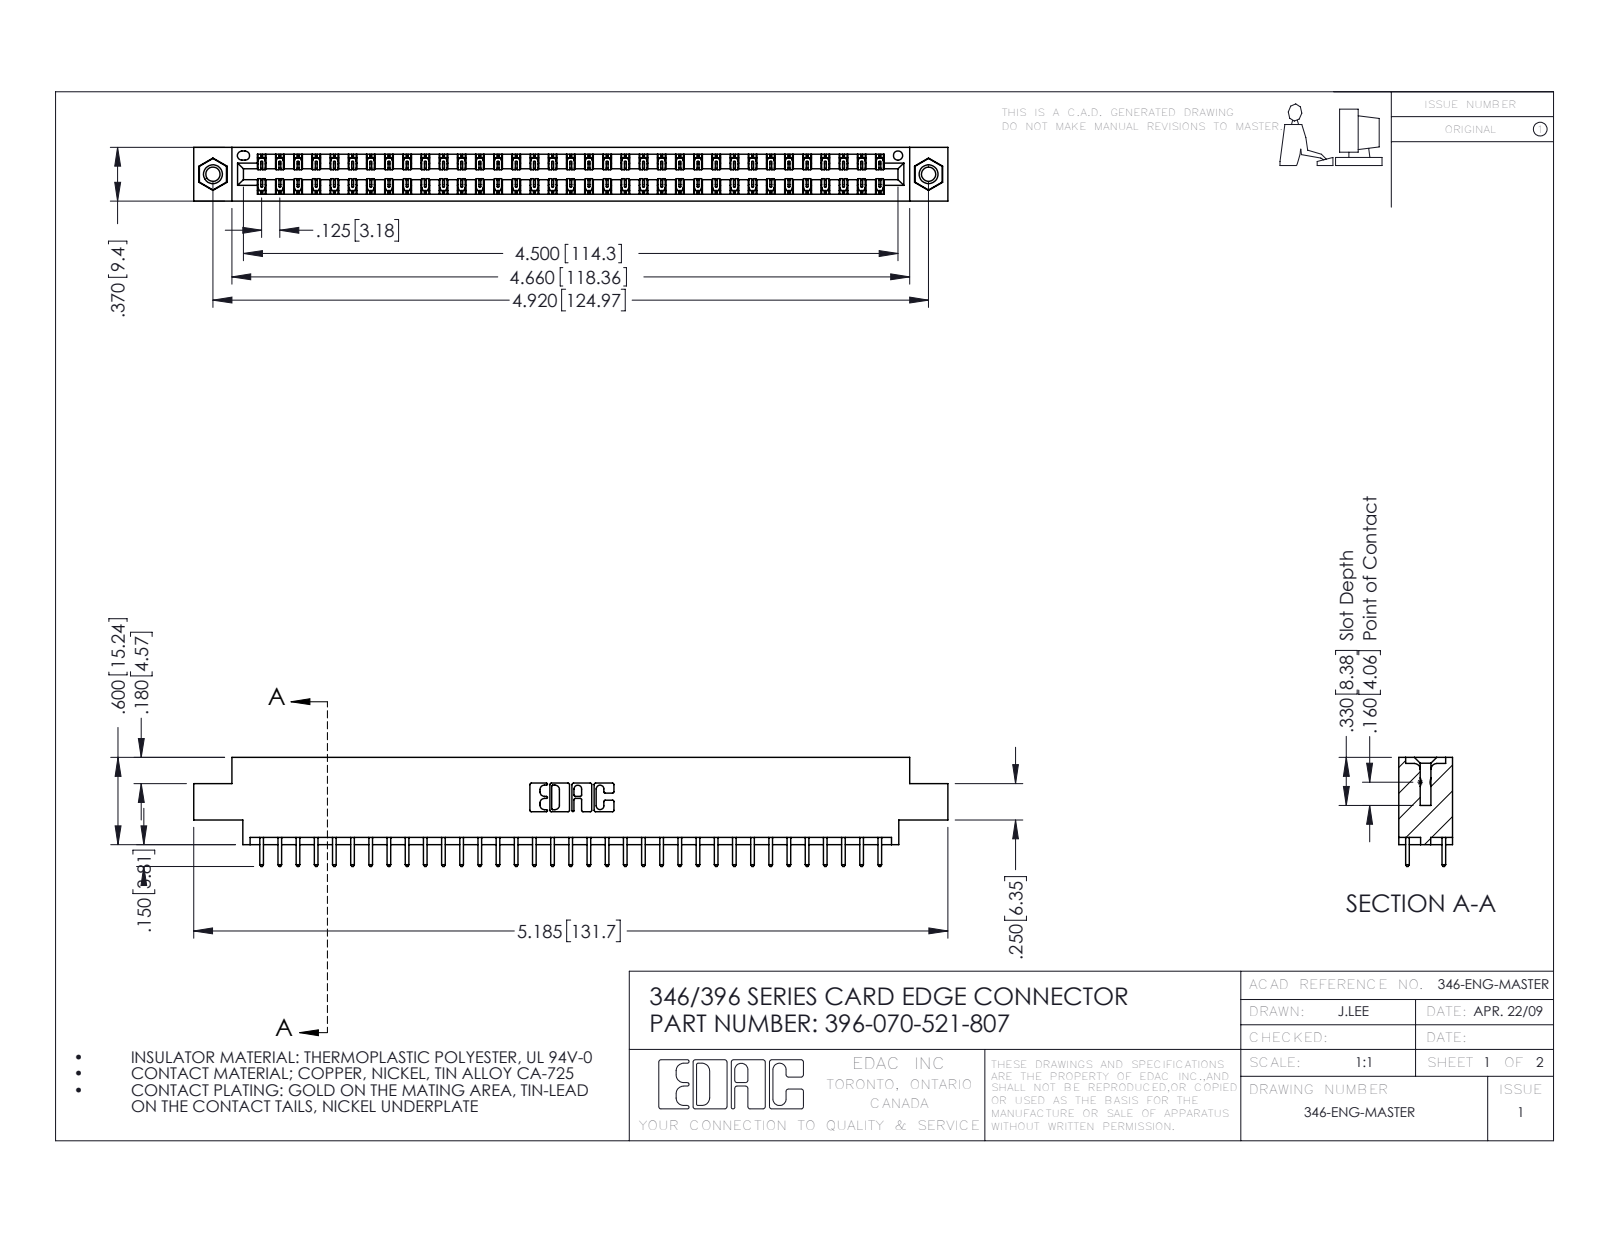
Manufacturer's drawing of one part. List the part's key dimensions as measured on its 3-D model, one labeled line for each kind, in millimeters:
Part name (STEP PRODUCT): 396-070-521-807; 345-292-001_345-293-121; 345-250-001_345-250-005-103; 346 Part_0.170 Offset - 0.156 Dia-TI
STEP written by: SolidWorks 2016 (CONFIG_CONTROL_DESIGN)
Units: millimetres
Bodies: 73 solids, 3826 faces (2562 planar, 1248 cylindrical, 16 other)
Overall size (bounding box): 131.7 × 19.1 × 9.4
Volume: 12 600 mm³ · Surface area: 17 220 mm²
Round holes (diameter × count): ⌀2.5 ×2, ⌀3.2 ×2, ⌀4 ×2, ⌀1.6 ×1
Round bosses / shafts (diameter × count): ⌀3.9 ×2
Partial cylindrical surfaces — rounded edges, fillets, slot ends (radius × count): R0.2 ×105, R0.3 ×70, R0.3 ×22, R0.2 ×6, R0.8 ×6, R0.7 ×3, R0.4 ×2, R0.6 ×2
Main face-to-face distances: 1.2, 8.2, 9.4, 6.4, 1.8, 7.6, 0.6, 7, 5.6, 3.8
Hole centre spacings: 6.2, 119.7, 125
